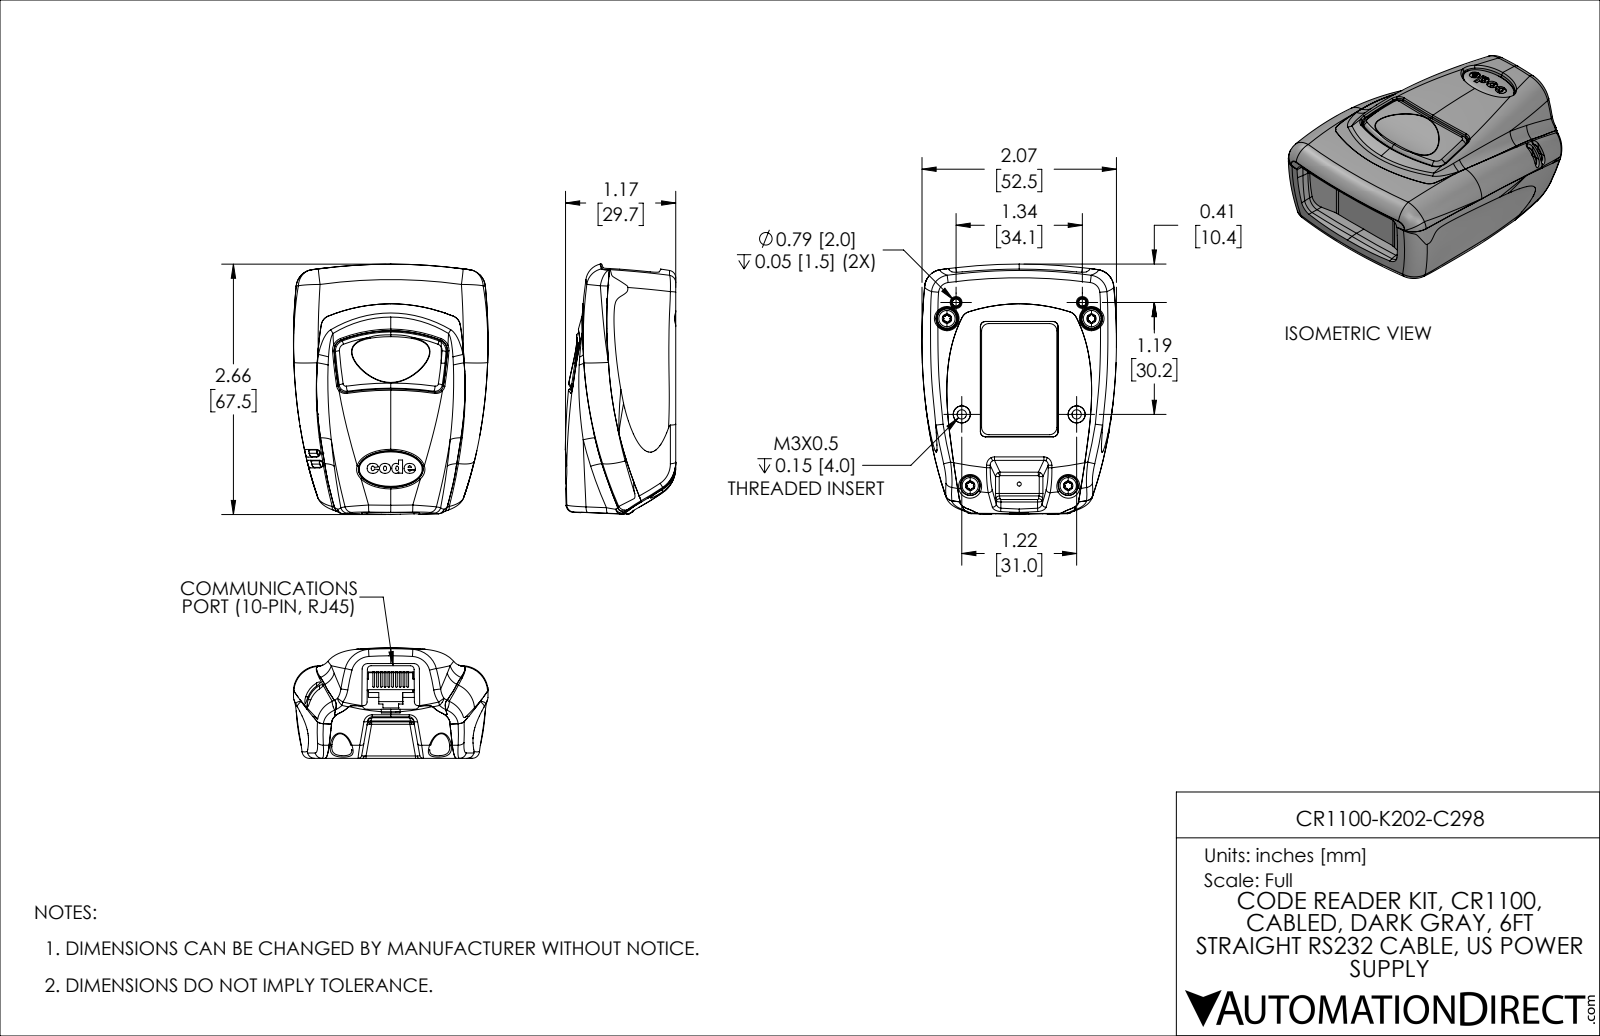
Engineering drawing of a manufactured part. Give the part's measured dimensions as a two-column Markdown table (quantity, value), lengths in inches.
| quantity | value |
| --- | --- |
| part name | CR1100 |
| STEP written by | SolidWorks 2019 (AUTOMOTIVE_DESIGN) |
| units | inches |
| bodies | 15 solids, 2758 faces (1018 planar, 514 cylindrical, 1226 other) |
| overall size | 2.66 × 2.067 × 1.174 |
| volume | 1.984 in³ |
| surface area | 69.18 in² |
| round holes (diameter × count) | 0.099 × 4, 0.098 × 2, 0.142 × 2, 0.15 × 2, 0.154 × 2, 0.165 × 2, 0.181 × 2, 0.043 × 1, 0.118 × 1 |
| round bosses / shafts (diameter × count) | 0.018 × 20, 0.173 × 4 |
| partial cylindrical surfaces (radius × count) | 0.012 × 43, 0.118 × 33, 0.009 × 28, 0.039 × 26, 0.017 × 24, 0.079 × 14, 0.02 × 8, 0.03 × 8 |
| main face-to-face distances | 0.118, 0.016, 0.102, 0.039, 0.059, 0.079, 0.112, 0.024, 0.02, 0.033 |
| hole center spacings | 0.521, 0.763, 0.77, 0.959, 1.029, 1.13, 1.361, 1.713 |
